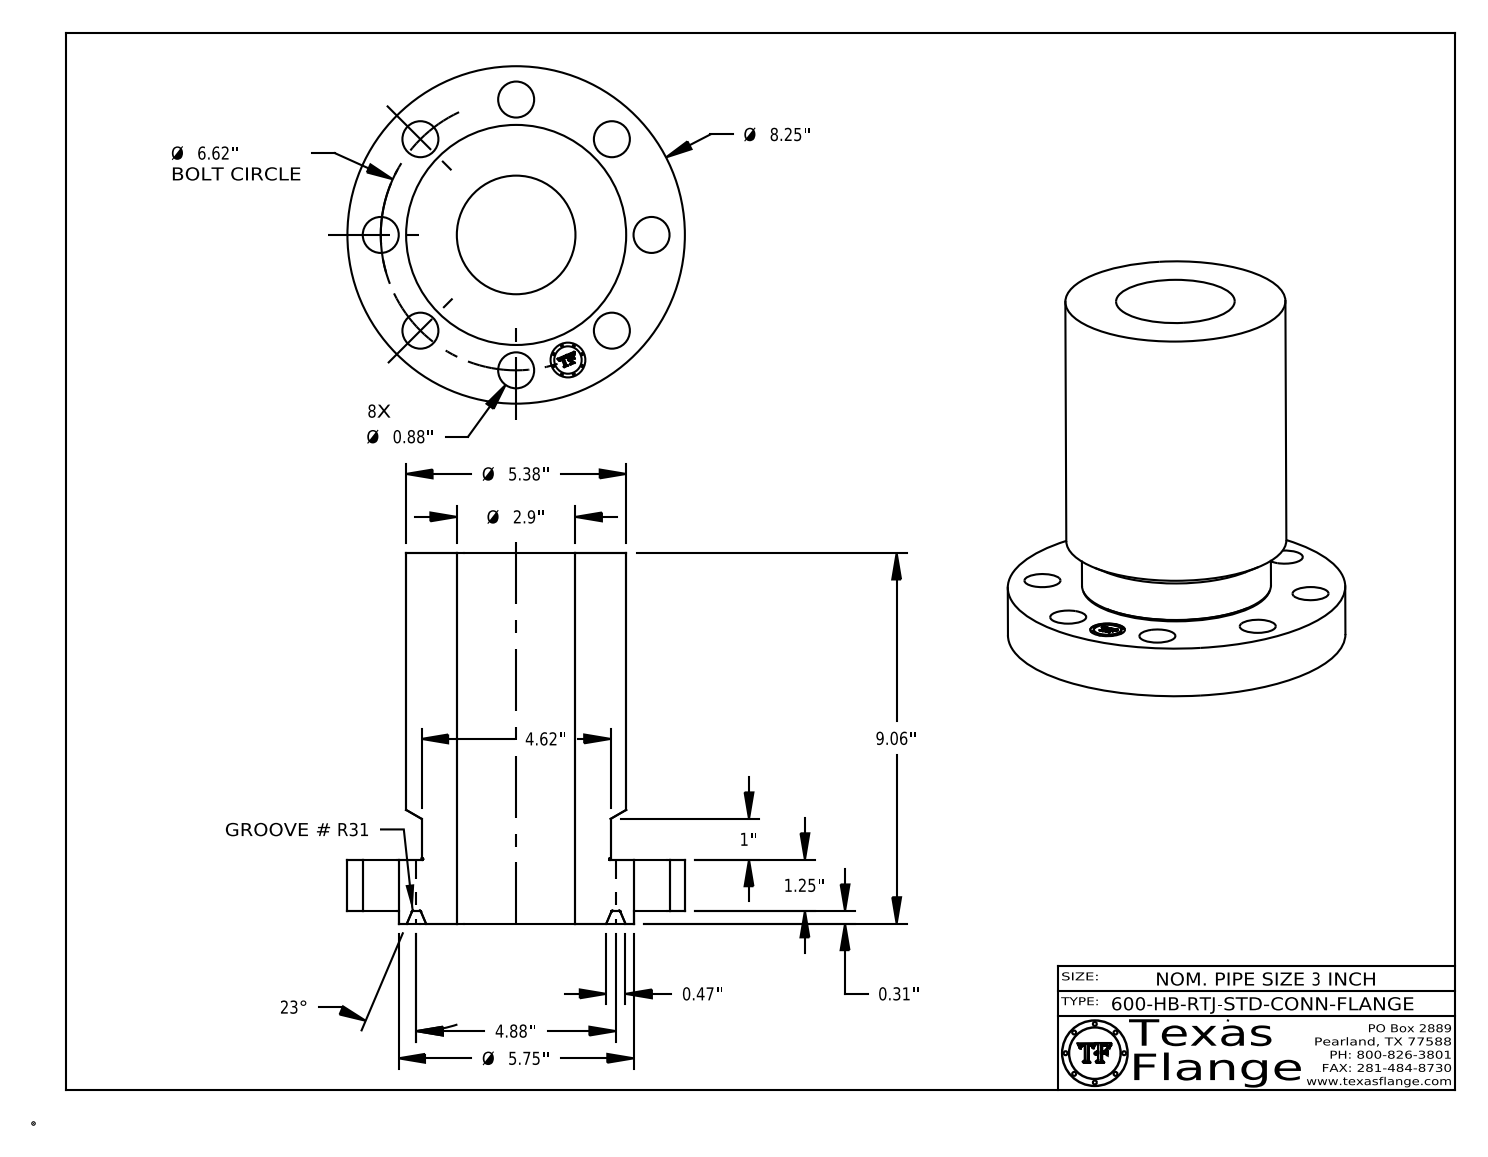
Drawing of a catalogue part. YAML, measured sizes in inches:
part_name: "3-600-HB-RTJ-STD-CONN-FLANGE"
step_written_by: "CATIA V5 STEP AP214 (AUTOMOTIVE_DESIGN)"
units: inches
bodies: {solids: 1, faces: 439, planar: 371, cylindrical: 54, other: 14}
overall_size: [9.063, 8.25, 8.25]
volume: 171.2
surface_area: 372.6
round_holes:
  - {diameter: 0.88, count: 8}
  - {diameter: 0.85, count: 1}
  - {diameter: 2.9, count: 1}
round_bosses_or_shafts:
  - {diameter: 0.051, count: 8}
  - {diameter: 8.25, count: 1}
  - {diameter: 5.75, count: 1}
  - {diameter: 5.38, count: 1}
  - {diameter: 4.62, count: 1}
  - {diameter: 0.67, count: 1}
face_to_face_distances: [1.25, 8.75, 7.5, 0.313, 1.563, 9.063, 1.558, 1.245, 7.505, 0.016]
hole_center_spacings: [3.31, 2.533, 6.116, 4.681, 4.681, 1.291, 3.678, 6.493]
